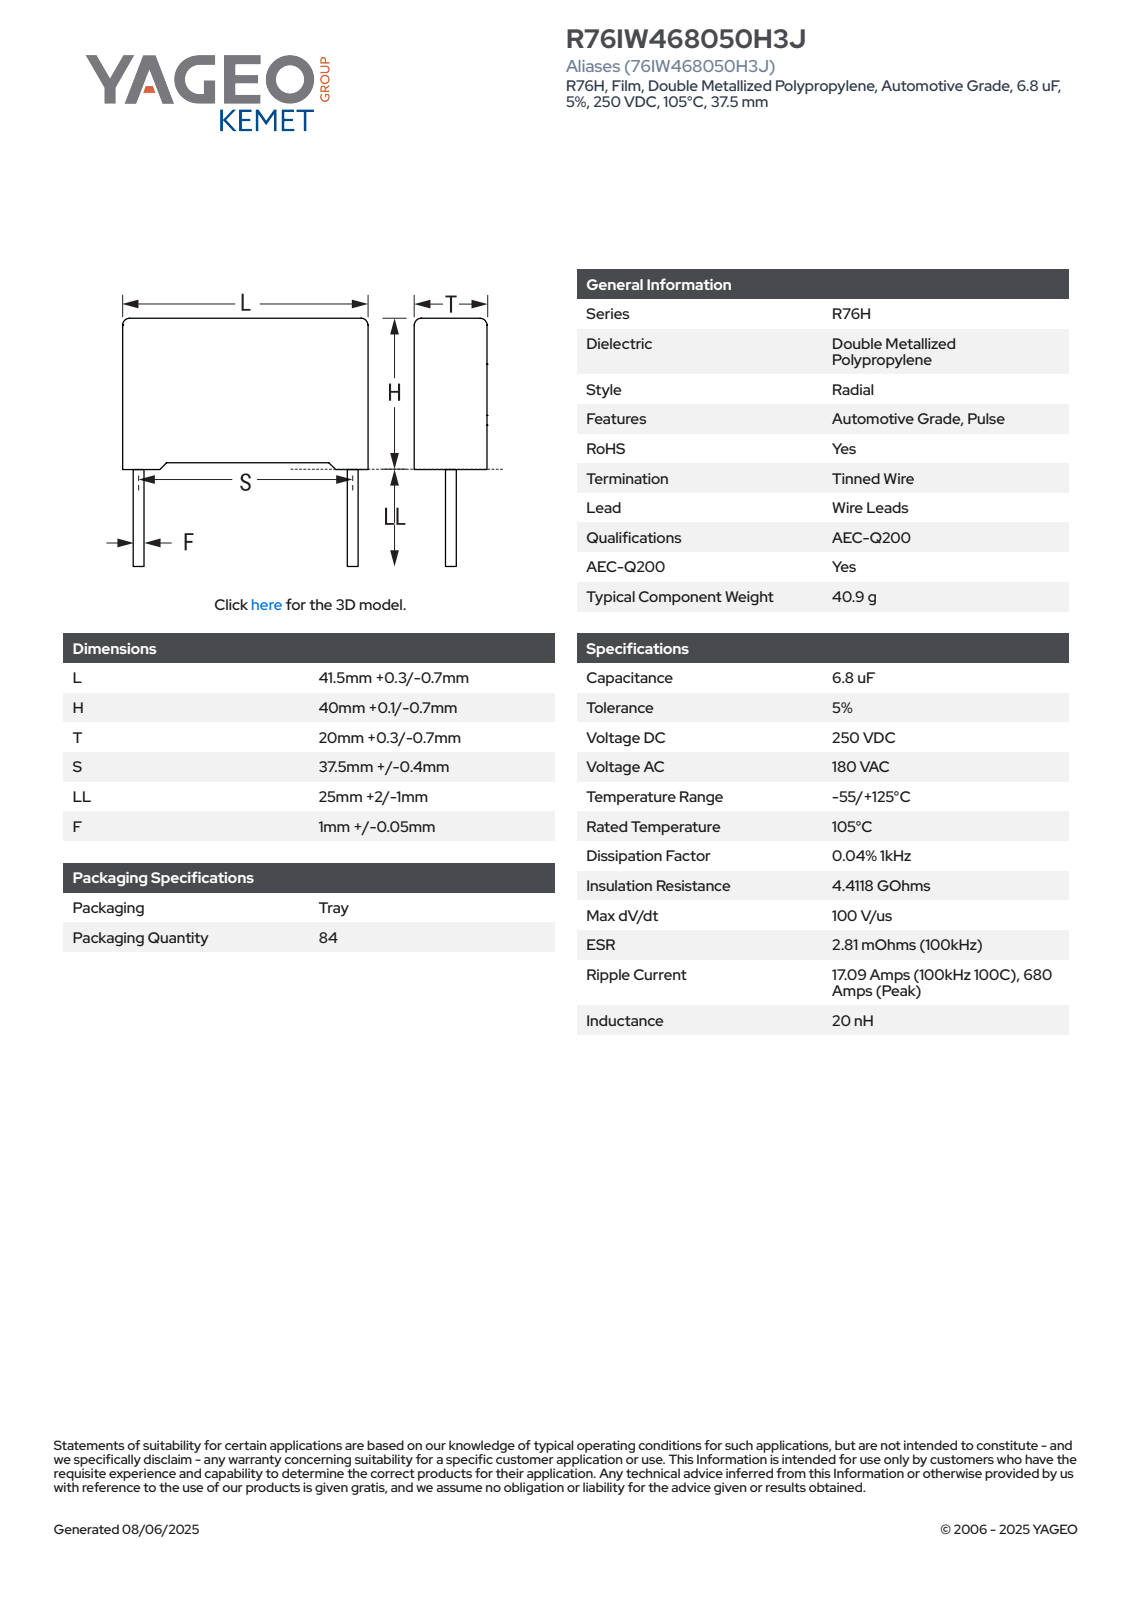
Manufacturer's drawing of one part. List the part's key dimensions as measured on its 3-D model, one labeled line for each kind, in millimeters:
Part name (STEP PRODUCT): CFR_RB2R76_41.5X40X20_L41.8H40.1T20.3S37.5LL27F1.05
STEP written by: SolidWorks 2014 (AUTOMOTIVE_DESIGN)
Units: millimetres
Bodies: 4 solids, 85 faces (77 planar, 8 cylindrical, 0 other)
Overall size (bounding box): 67.1 × 41.8 × 20.3
Volume: 33 065 mm³ · Surface area: 6 920 mm²
Round bosses / shafts (diameter × count): ⌀1.05 ×2
Partial cylindrical surfaces — rounded edges, fillets, slot ends (radius × count): R0.5 ×4
Main face-to-face distances: 20.3, 41.8, 38.72, 0.63, 39.35, 0.75, 1.38, 40.1, 1.39, 20.31
